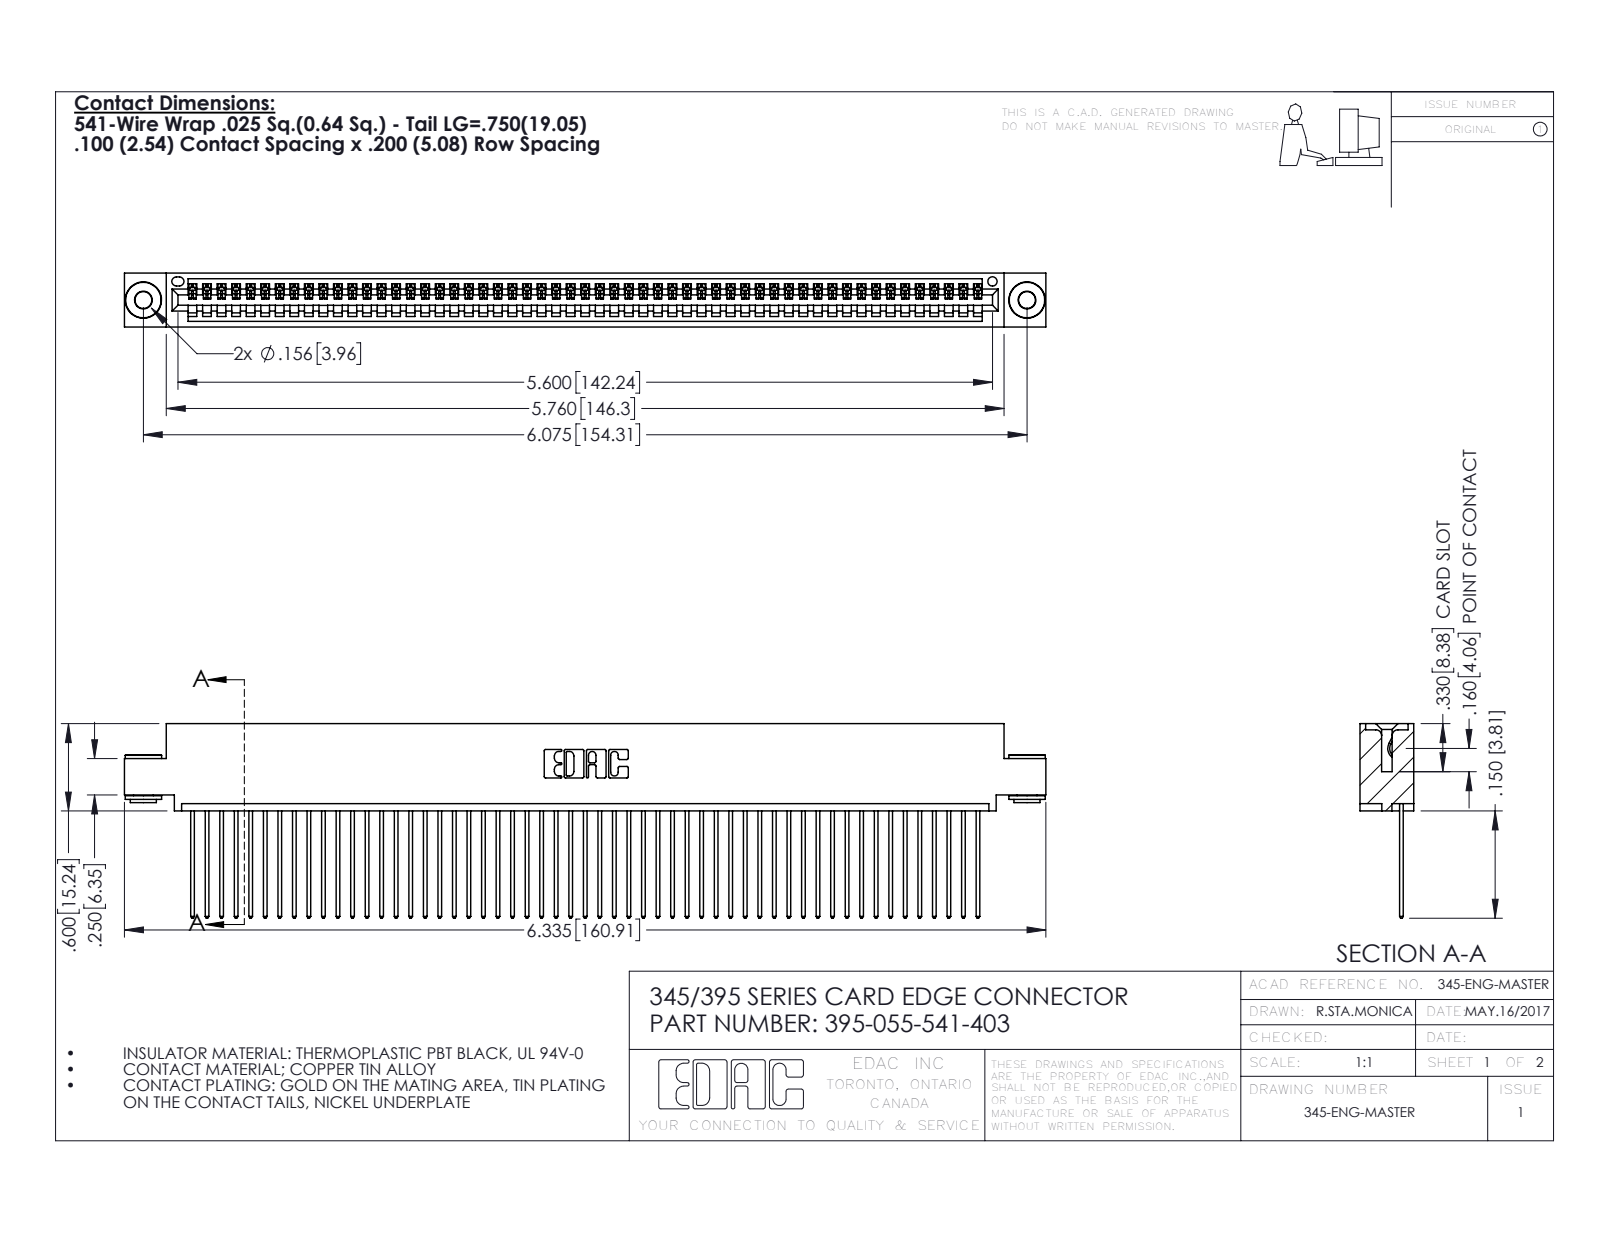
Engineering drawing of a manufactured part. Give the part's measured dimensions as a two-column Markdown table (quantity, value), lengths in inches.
| quantity | value |
| --- | --- |
| part name | 395-055-541-403; 345 Part_0.110 Offset - 0.156 Dia-TH; 345-250-002_345-250-002-102; 345-292-001_345-293-141 |
| STEP written by | SolidWorks 2016 (CONFIG_CONTROL_DESIGN) |
| units | inches |
| bodies | 58 solids, 3358 faces (2294 planar, 1056 cylindrical, 8 other) |
| overall size | 6.335 × 1.337 × 0.37 |
| volume | 0.947 in³ |
| surface area | 34.35 in² |
| round holes (diameter × count) | 0.116 × 2, 0.156 × 2, 0.064 × 1 |
| round bosses / shafts (diameter × count) | 0.25 × 2, 0.18 × 2, 0.136 × 2 |
| partial cylindrical surfaces (radius × count) | 0.006 × 110, 0.01 × 110, 0.01 × 22, 0.007 × 6, 0.031 × 6, 0.026 × 3, 0.031 × 2, 0.04 × 2 |
| main face-to-face distances | 0.072, 0.298, 0.025, 0.098, 0.272, 0.37, 0.2, 0.225, 0.149, 0.072 |
| hole center spacings | 0.27, 5.839, 6.075 |
